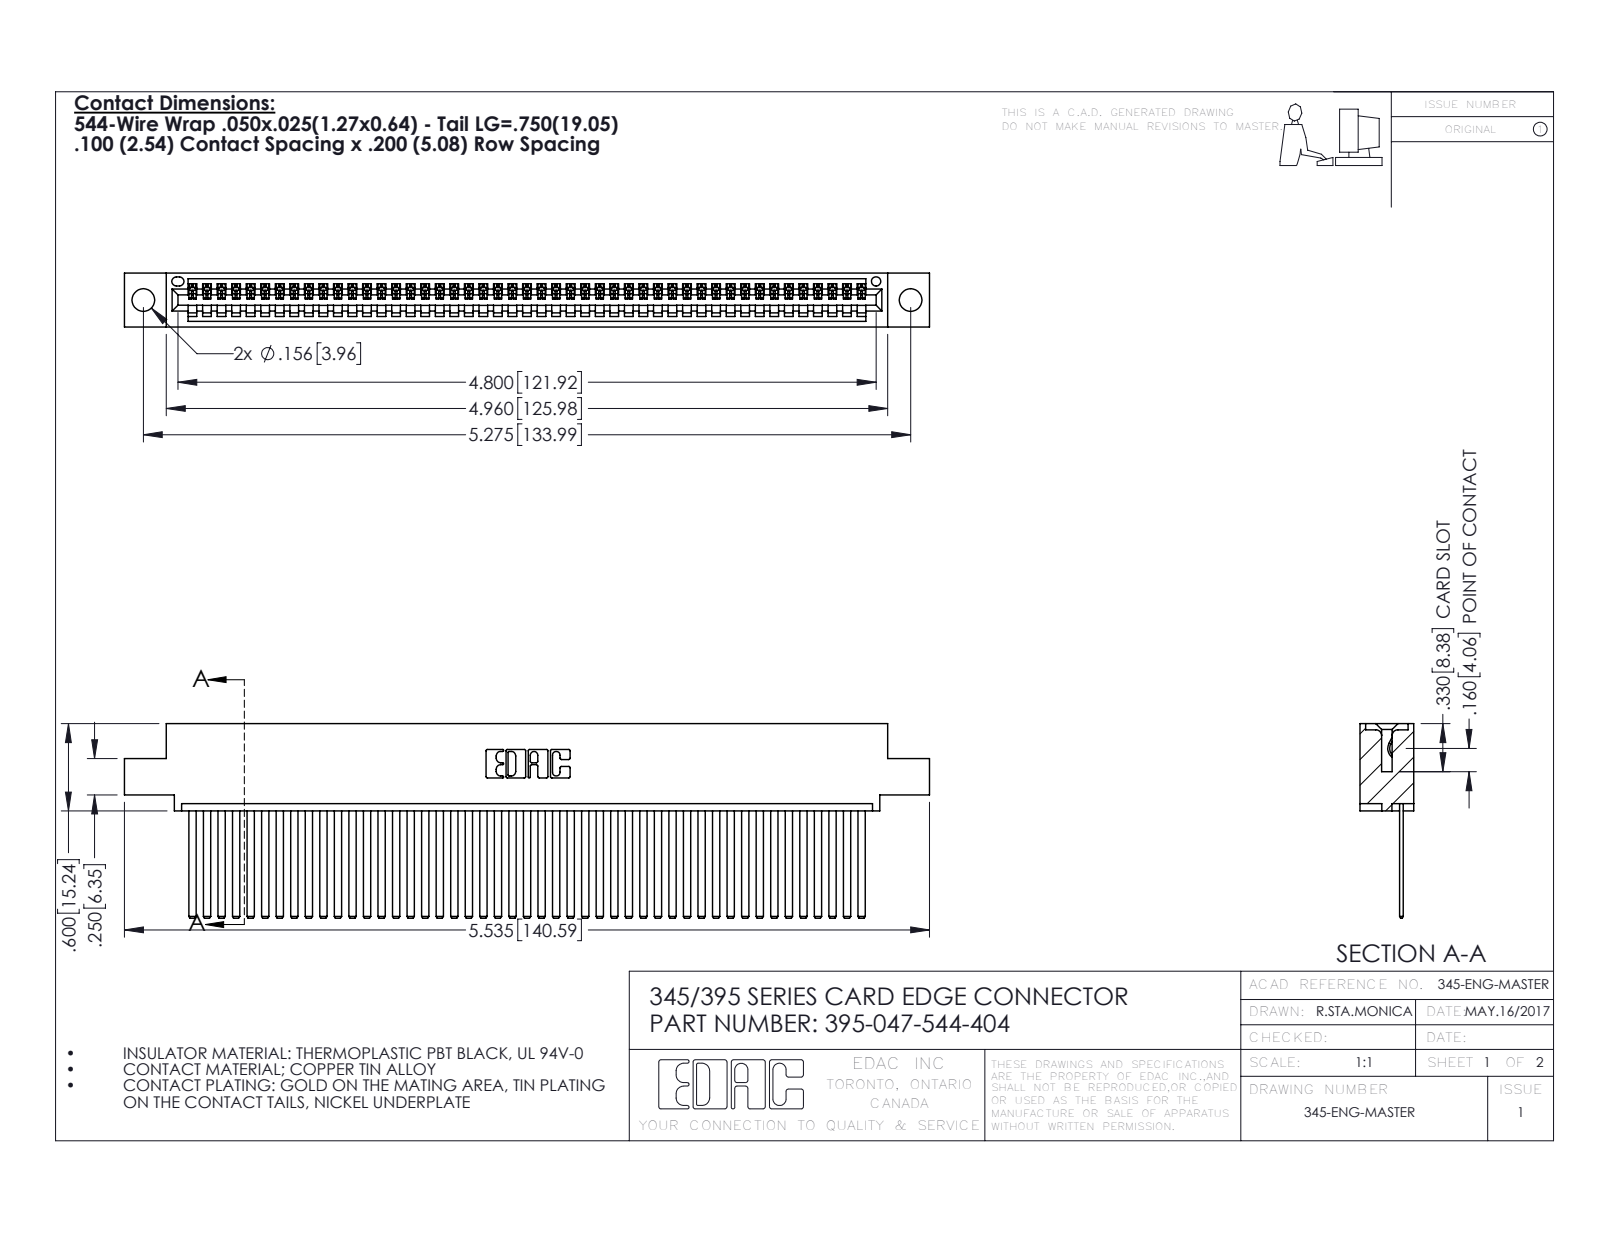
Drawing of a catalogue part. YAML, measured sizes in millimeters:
part_name: "345 Part_0.110 Offset - 0.156 Dia-TH; 395-047-544-404; 345-292-001_345-293-144"
step_written_by: "SolidWorks 2016 (CONFIG_CONTROL_DESIGN)"
units: millimeters
bodies: {solids: 48, faces: 2574, planar: 1776, cylindrical: 798, other: 0}
overall_size: [140.6, 34, 9.4]
volume: 13800
surface_area: 19900
round_holes:
  - {diameter: 4, count: 2}
  - {diameter: 1.6, count: 1}
partial_cylinders:
  - {radius: 0.2, count: 94}
  - {radius: 0.3, count: 22}
  - {radius: 0.2, count: 6}
  - {radius: 0.8, count: 6}
  - {radius: 0.7, count: 3}
  - {radius: 0.8, count: 2}
  - {radius: 1, count: 2}
  - {radius: 0.4, count: 1}
face_to_face_distances: [1.8, 7.6, 0.6, 2.5, 6.9, 9.4, 5.1, 5.7, 3.8, 1.8]
hole_center_spacings: [6.9, 128, 134]
